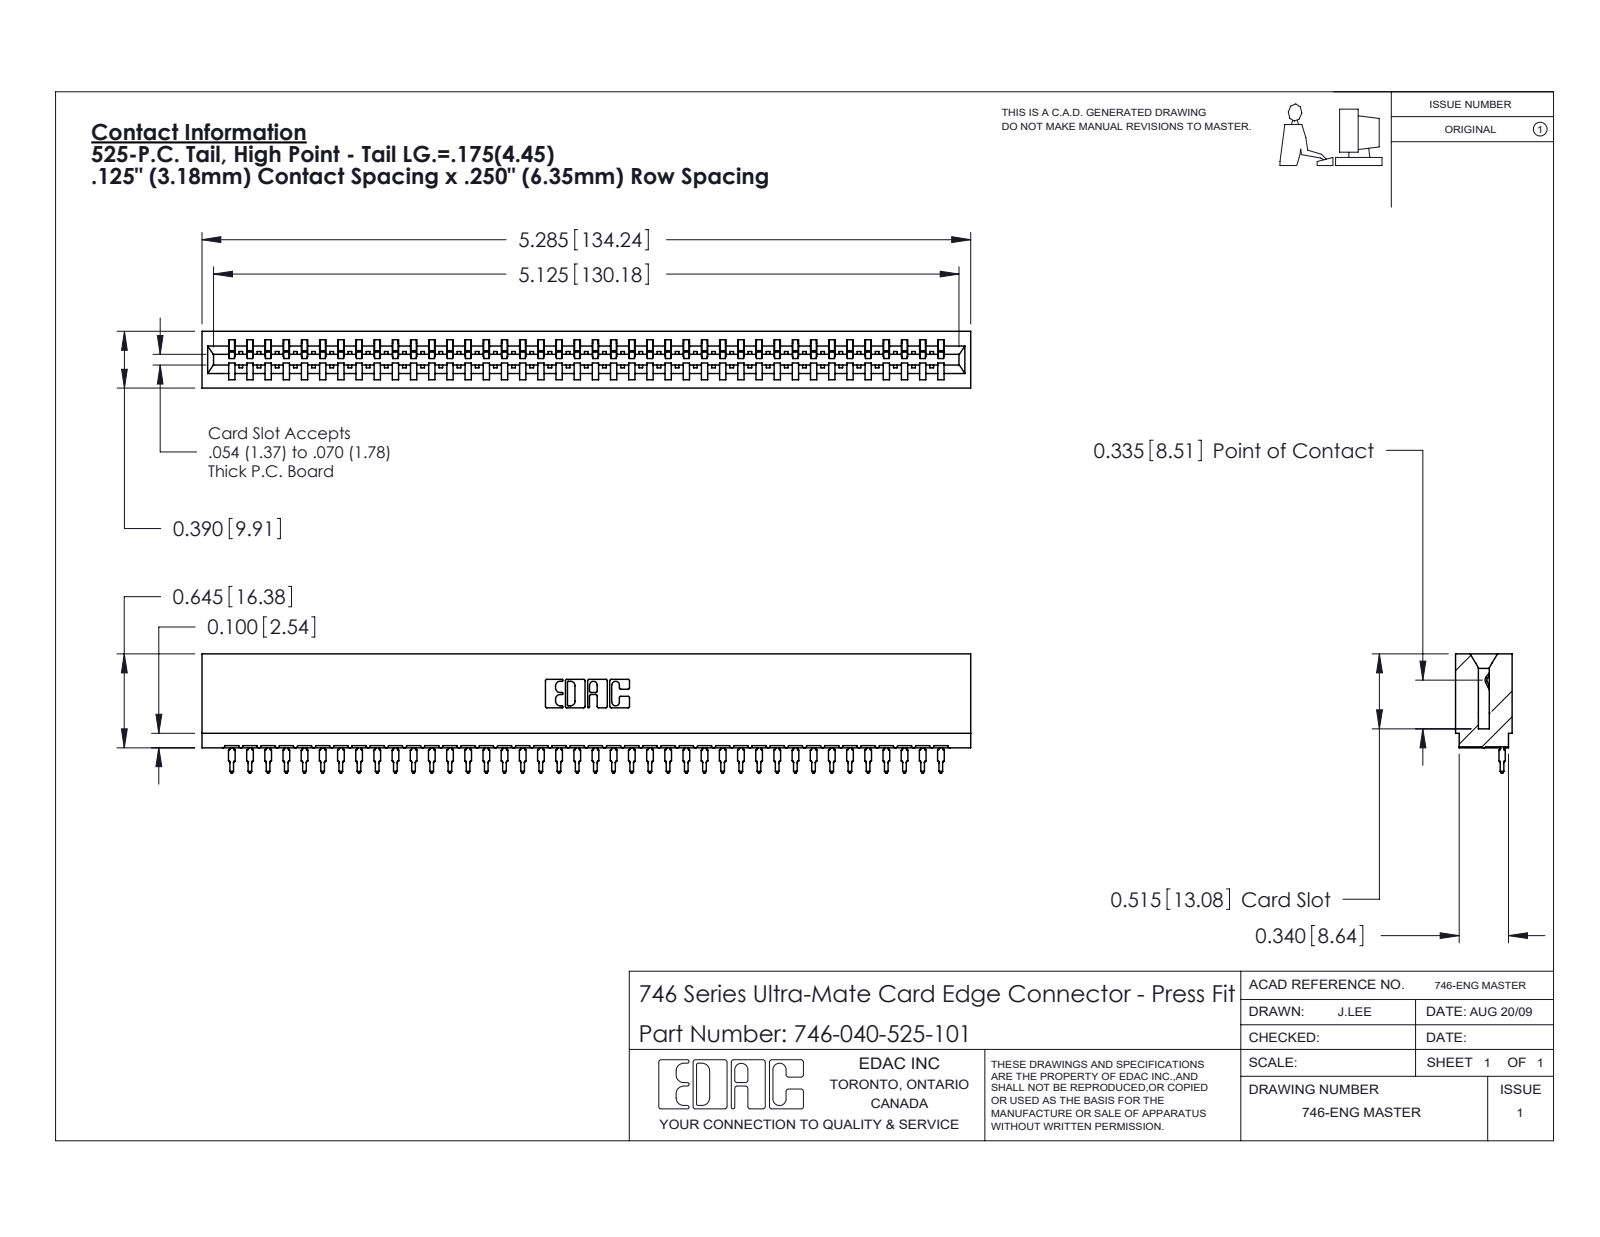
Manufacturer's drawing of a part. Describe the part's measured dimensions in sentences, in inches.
The part is named "746 Part_.515 Slot Depth - 01; 746-040-525-101; 746-292-001_525". Its 3-D file was written by "SolidWorks 2020 (CONFIG_CONTROL_DESIGN)". It is 41 solids with 4417 faces: 2575 planar, 802 cylindrical and 1040 other. Overall it measures 5.285 by 0.819 by 0.39 inches. Its volume is 0.853 cubic inches and its surface area 31.8 square inches. Partial cylindrical surfaces (rounded edges, fillets, slot ends): 80 of radius 0.021, 41 of radius 0.015, 22 of radius 0.01, 6 of radius 0.007, 6 of radius 0.031, 4 of radius 0.005, 4 of radius 0.011, 3 of radius 0.026. The main face-to-face distances are 0.057, 0.333, 0.39, 0.25, 0.025, 0.307, 0.275, 0.5, 0.174, 0.158.
